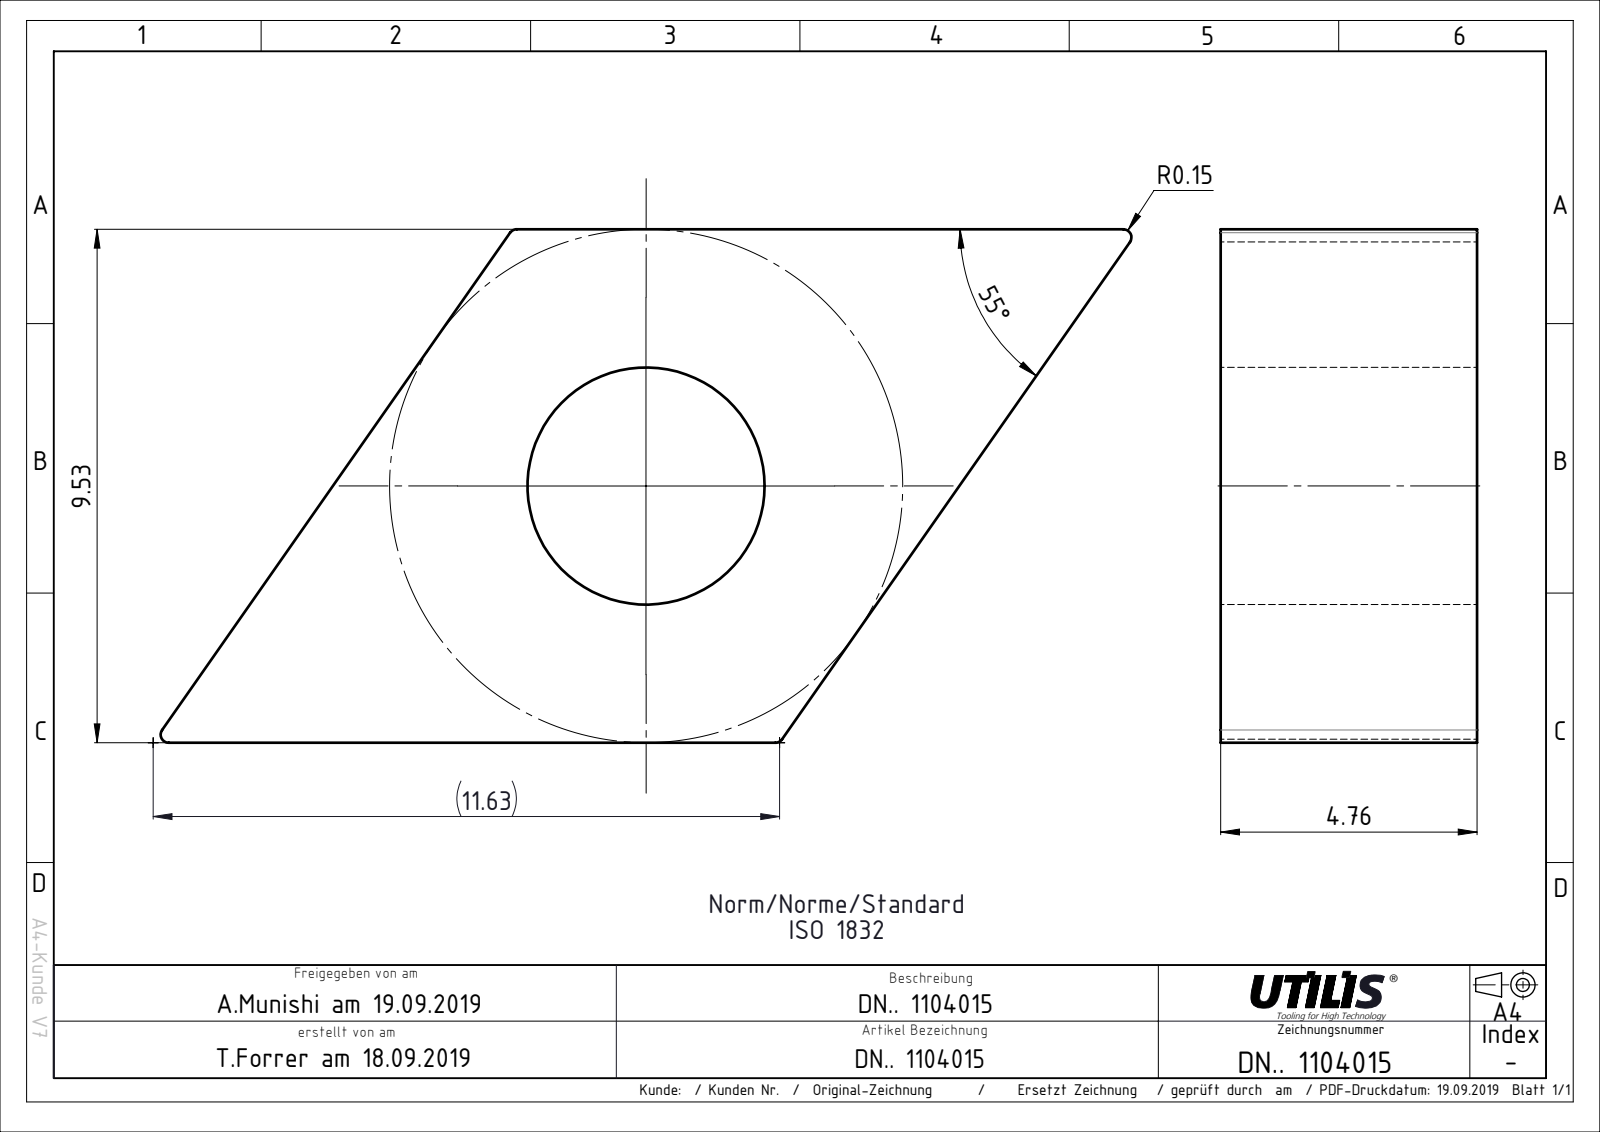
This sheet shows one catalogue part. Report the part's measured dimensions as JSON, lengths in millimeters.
{"part_name": "DN.. 1104015", "step_written_by": "SolidWorks 2016 (AUTOMOTIVE_DESIGN)", "units": "millimeters", "bodies": {"solids": 1, "faces": 13, "planar": 6, "cylindrical": 7, "other": 0}, "overall_size": [18.02, 9.53, 4.76], "volume_mm3": 455, "surface_area_mm2": 476, "round_holes": [[4.4, 1]], "partial_cylinders_radius": [[0.15, 4]], "face_to_face_distances": [9.52, 4.76]}
